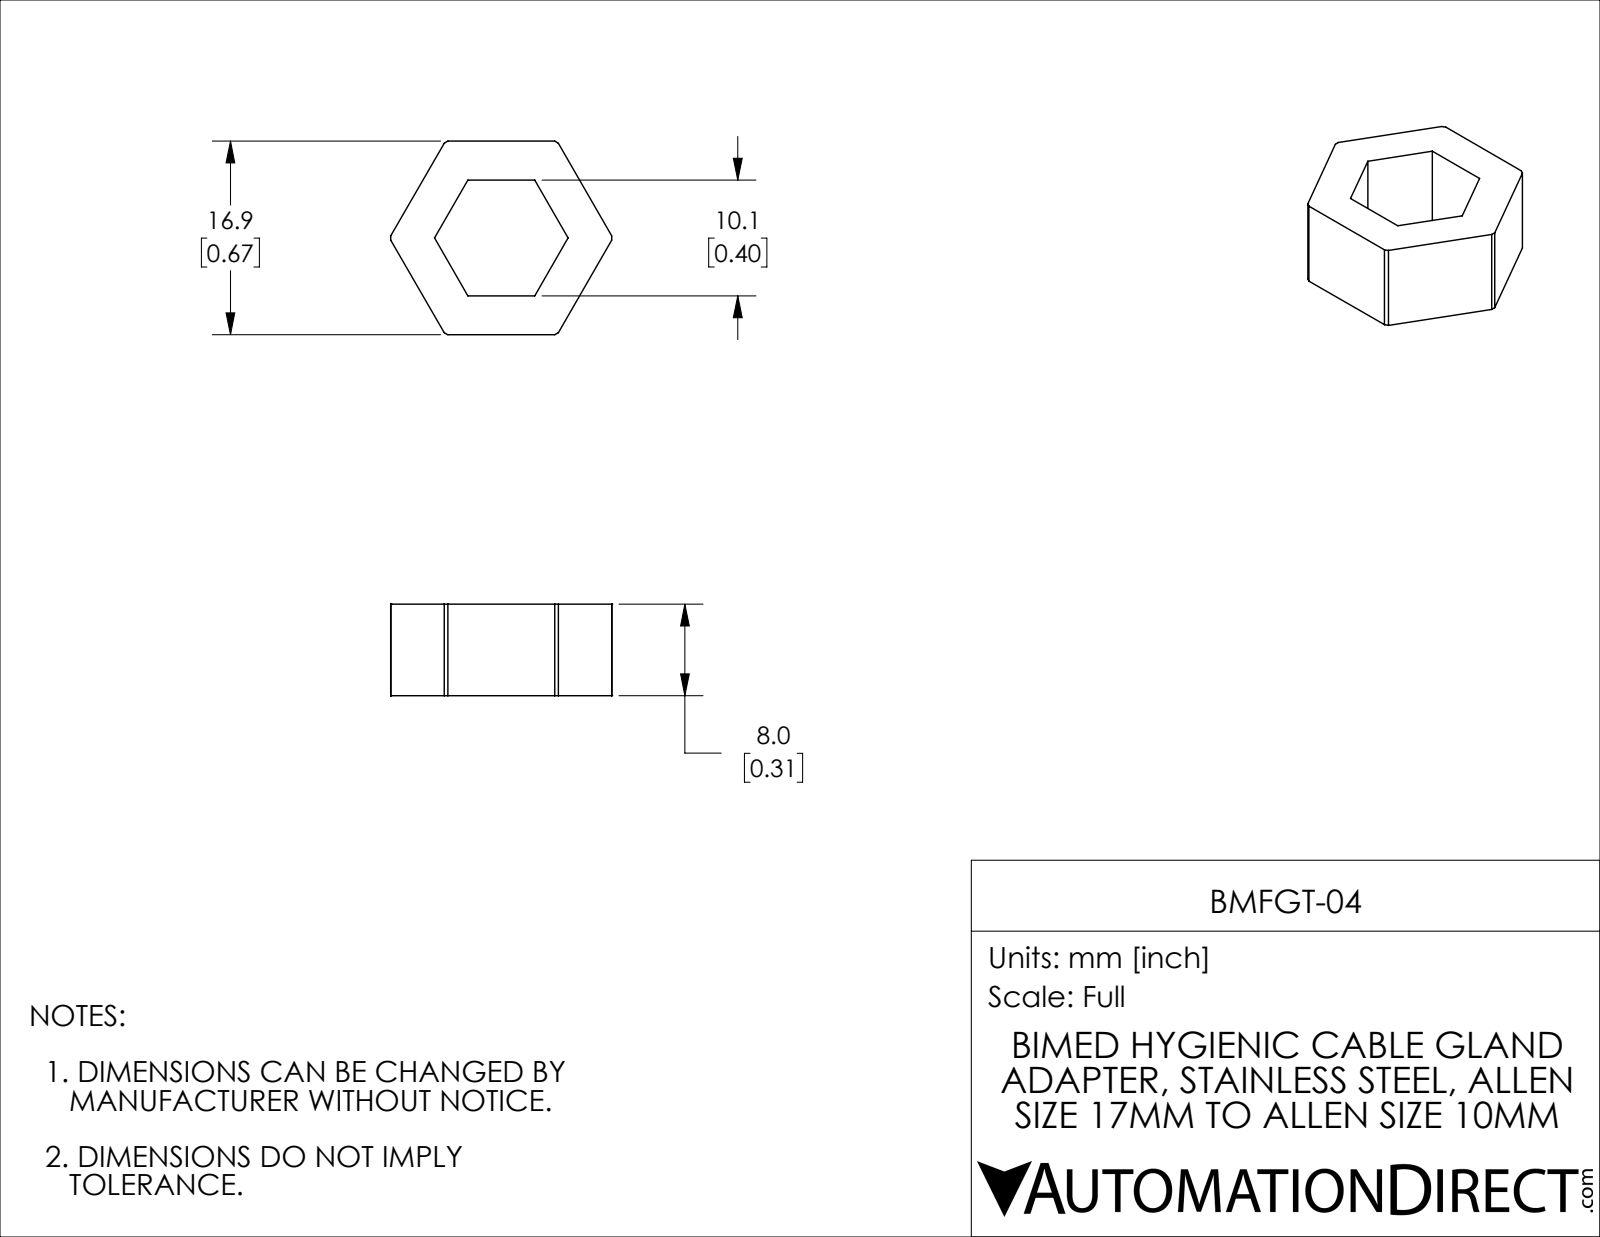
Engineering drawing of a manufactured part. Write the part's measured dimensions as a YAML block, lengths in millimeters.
part_name: "BMFGT-04"
step_written_by: "SolidWorks 2021 (CONFIG_CONTROL_DESIGN)"
units: millimeters
bodies: {solids: 1, faces: 22, planar: 14, cylindrical: 8, other: 0}
overall_size: [19.3, 16.9, 8]
volume: 1271
surface_area: 1063
partial_cylinders:
  - {radius: 9.65, count: 1}
face_to_face_distances: [3.4, 13.5, 16.9, 8, 10.1]
